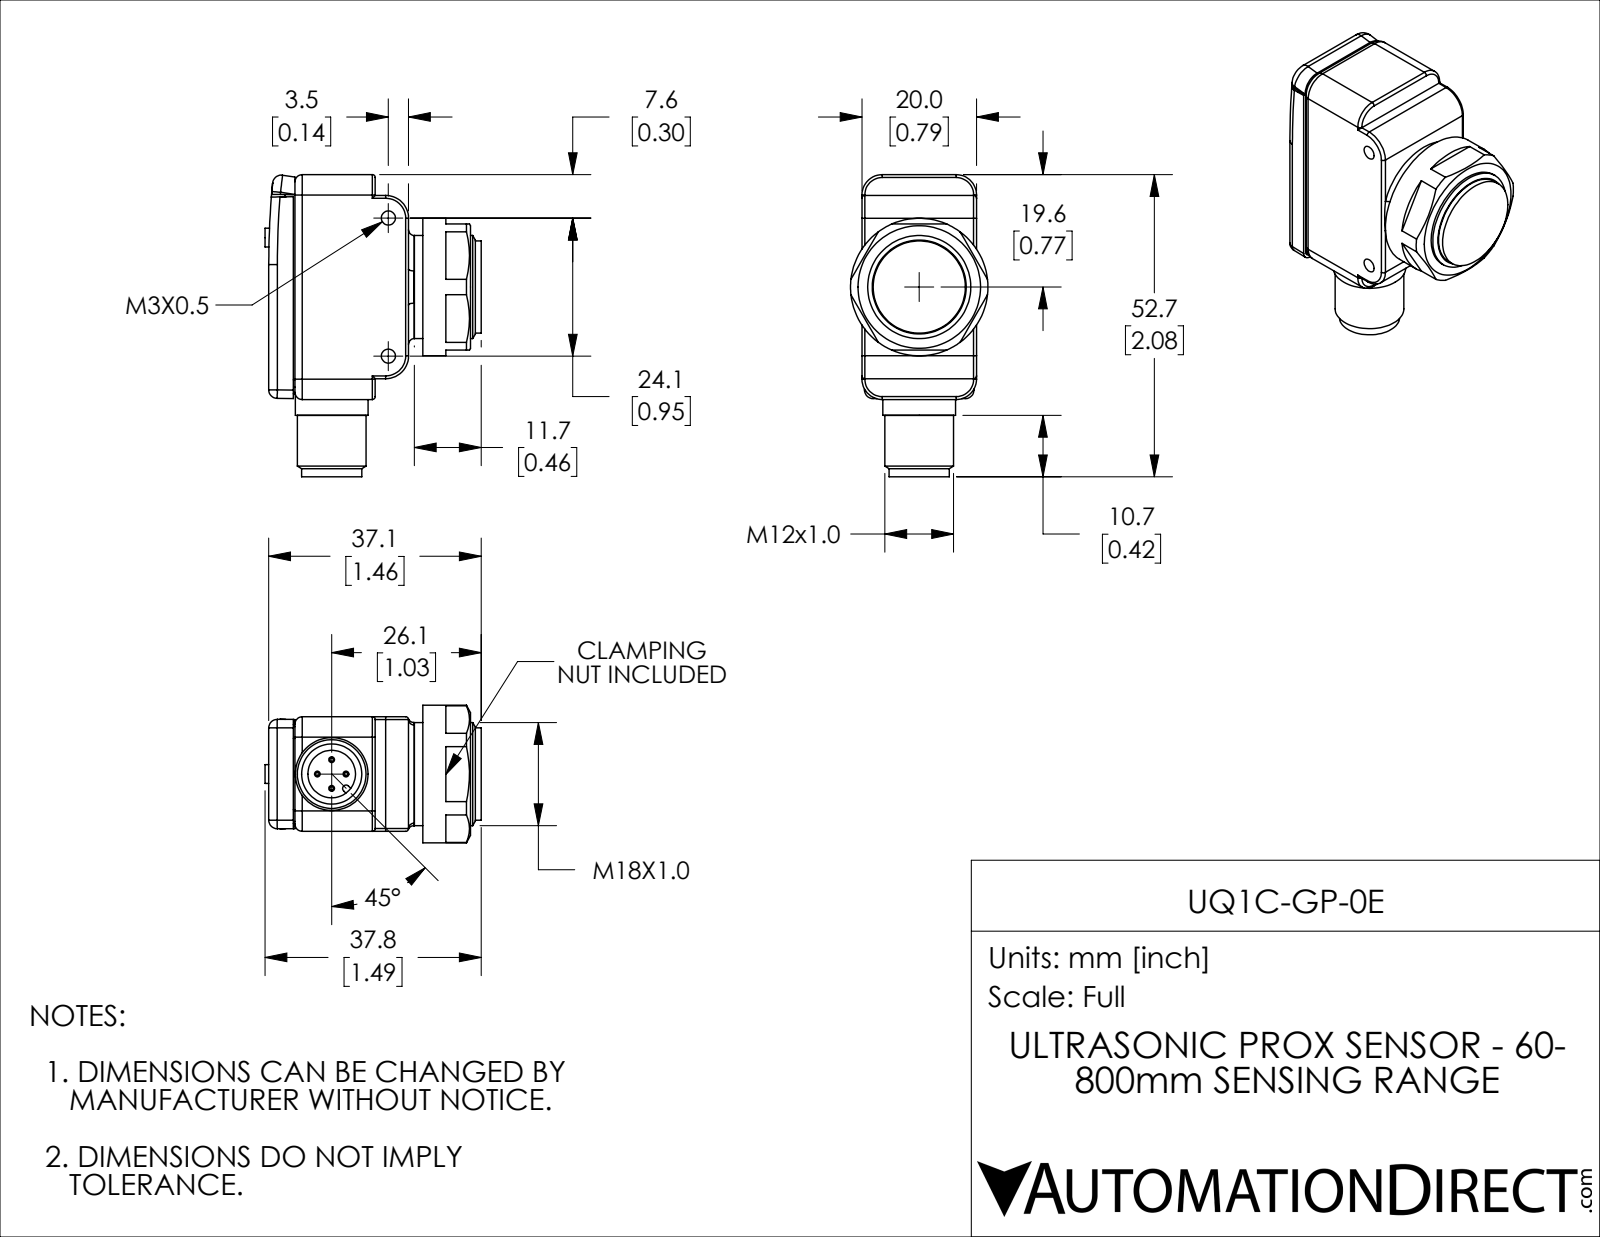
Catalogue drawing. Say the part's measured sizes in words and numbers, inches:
The part is named "UQ1C-GP-0E". Its 3-D file was written by "SolidWorks 2018 (AUTOMOTIVE_DESIGN)". It is 7 solids with 203 faces: 81 planar, 72 cylindrical and 50 other. Overall it measures 2.076 by 1.486 by 0.945 inches. Its volume is 1.389 cubic inches and its surface area 17.13 square inches. Round holes: 2 of diameter 0.097, 1 of diameter 0.13, 1 of diameter 0.327. Round bosses or shafts: 4 of diameter 0.039, 1 of diameter 0.945, 1 of diameter 0.709, 1 of diameter 0.634, 1 of diameter 0.5, 1 of diameter 0.472, 1 of diameter 0.413. Partial cylindrical surfaces (rounded edges, fillets, slot ends): 10 of radius 0.02, 6 of radius 0.059, 4 of radius 0.049, 4 of radius 0.14, 2 of radius 0.118, 2 of radius 0.157, 2 of radius 5.906, 1 of radius 0.024. The main face-to-face distances are 0.091, 0.787, 0.911, 0.82, 0.09, 0.181, 1.001, 0.459, 1.46, 1.37. The hole center spacings are 0.949.
